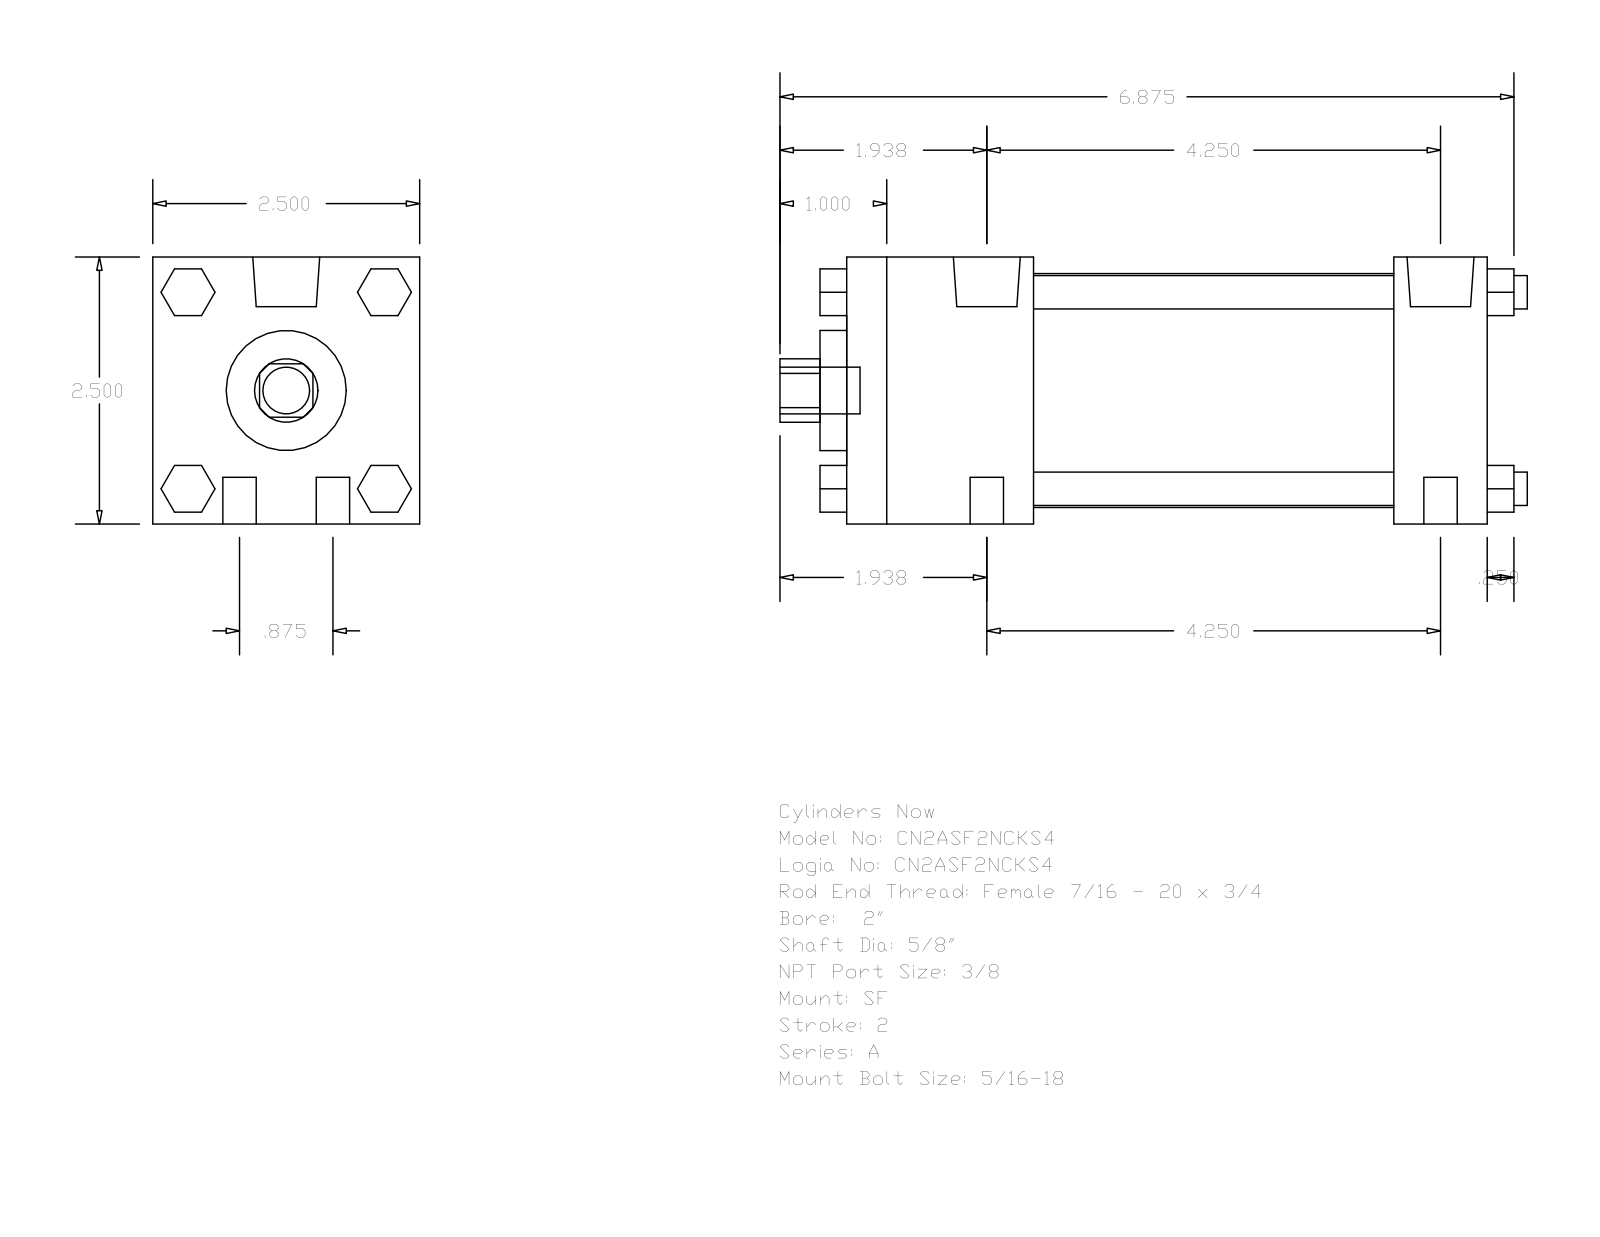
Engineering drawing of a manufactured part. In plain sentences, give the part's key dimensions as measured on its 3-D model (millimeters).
The part is named "A_SF__0200_0.625". Its 3-D file was written by "GSSL Pune (CONFIG_CONTROL_DESIGN)". It is 0 solids with 124 faces: 94 planar, 30 cylindrical and 0 other. Overall it measures 177.8 by 63.5 by 63.5 millimeters. Round holes: 1 of diameter 15.88, 1 of diameter 28.57, 1 of diameter 55.63. Round bosses or shafts: 8 of diameter 7.94, 2 of diameter 15.93, 2 of diameter 5.56, 1 of diameter 11.11. Partial cylindrical surfaces (rounded edges, fillets, slot ends): 1 of radius 7.54. The main face-to-face distances are 63.5, 152.4, 130.17, 22.23, 44.45, 85.72, 107.95, 50.8, 158.75, 6.35.
